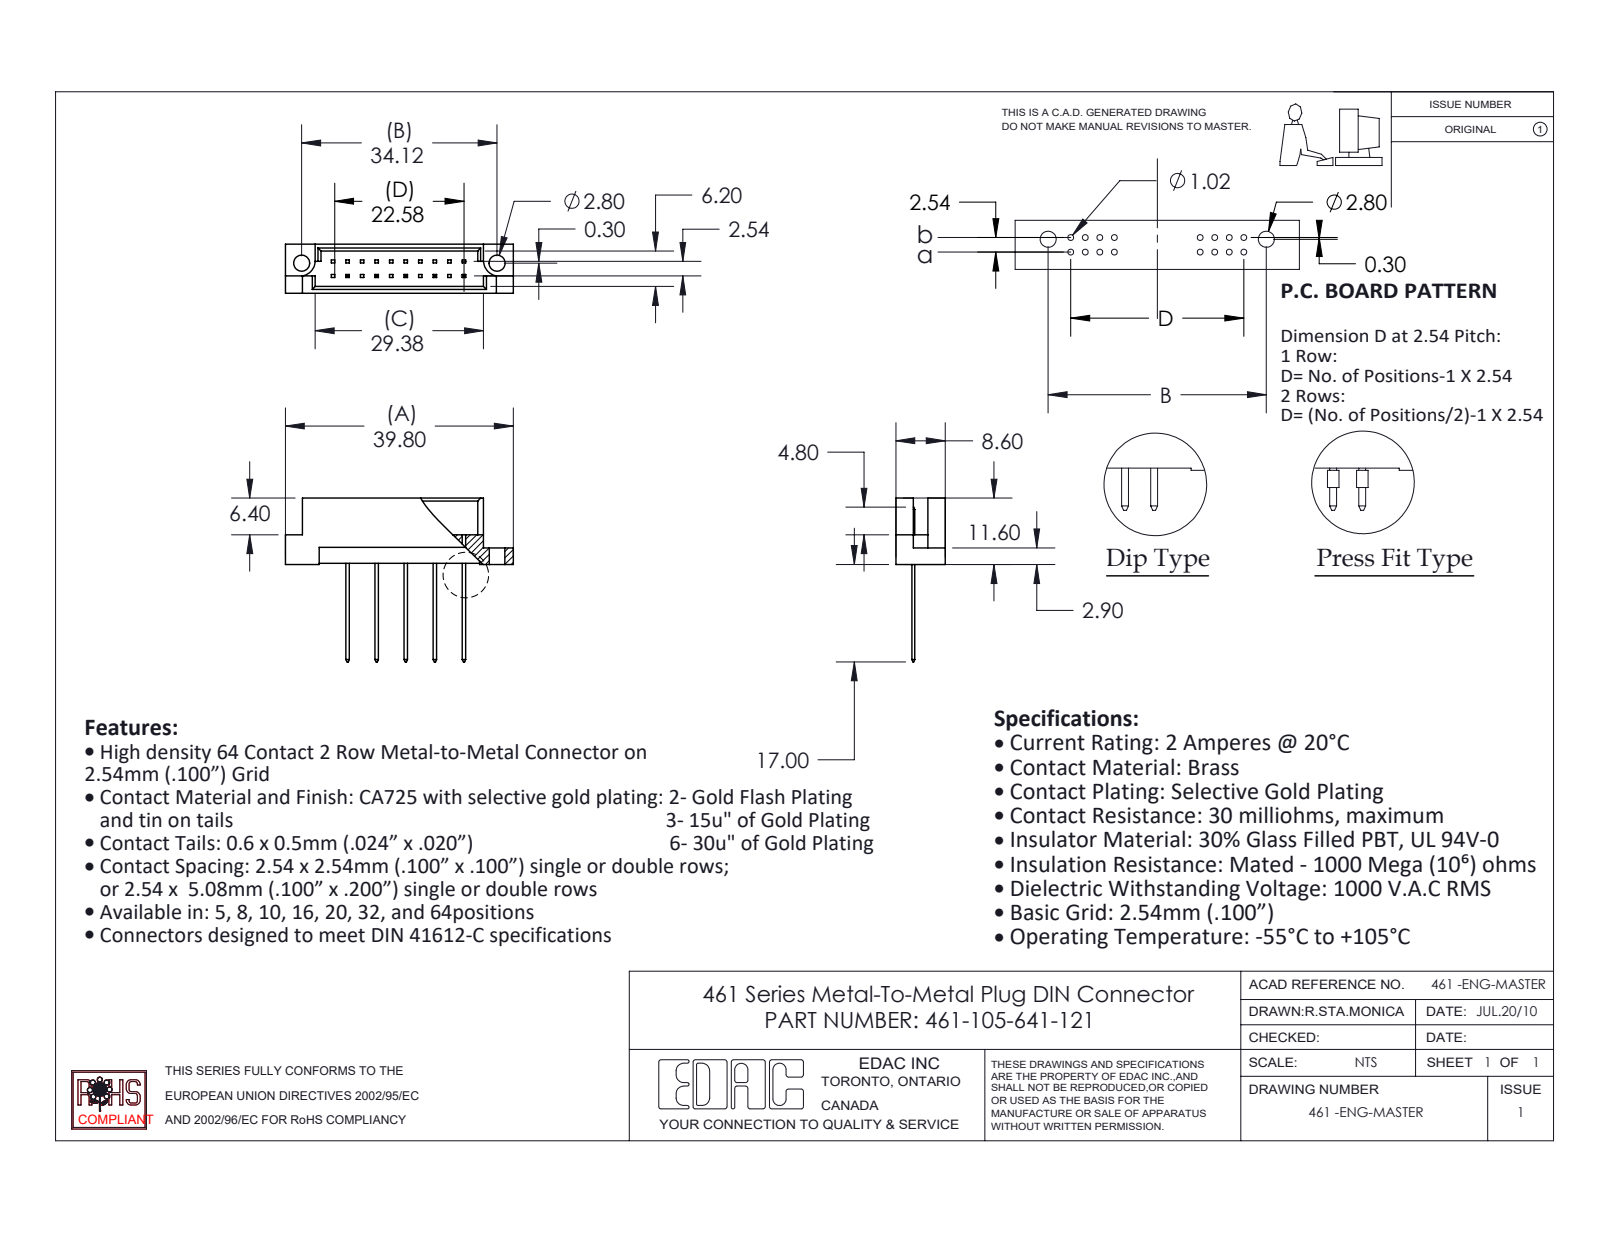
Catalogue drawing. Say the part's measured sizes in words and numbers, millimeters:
The part is named "461-290_41; 461-105-641-121; 461 Part_20". Its 3-D file was written by "SolidWorks 2020 (CONFIG_CONTROL_DESIGN)". It is 6 solids with 198 faces: 192 planar, 6 cylindrical and 0 other. Overall it measures 39.8 by 28.6 by 8.6 millimeters. Its volume is 1 945 cubic millimeters and its surface area 2 633 square millimeters. Round holes: 2 of diameter 2.8. Partial cylindrical surfaces (rounded edges, fillets, slot ends): 2 of radius 2.8. The main face-to-face distances are 1.2, 7.4, 8.6, 6.2, 5, 5.08, 2.78, 3.28, 5.32, 5.82. The hole center spacings are 34.12.
